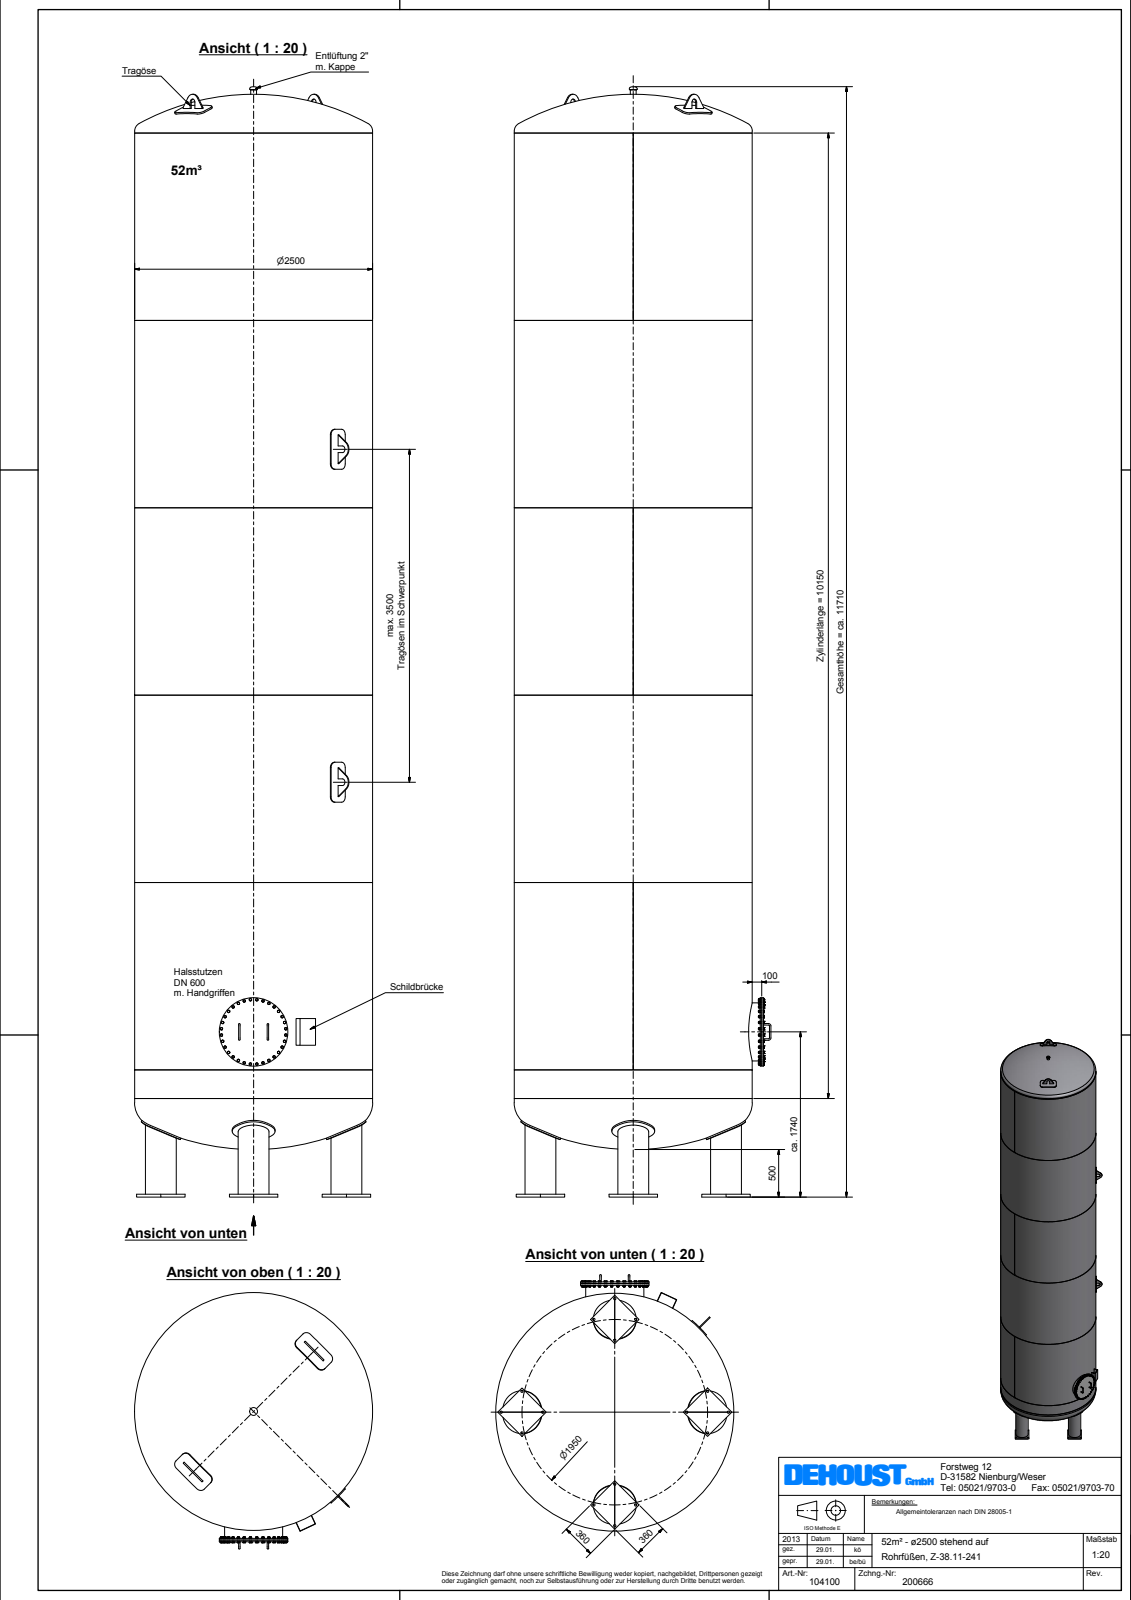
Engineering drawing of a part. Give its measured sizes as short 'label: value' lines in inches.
name: Beh\S\dlter_Z-38_11-241_2500_052_KV
written by: Autodesk Inventor 2012 (AUTOMOTIVE_DESIGN)
unit: in
bodies: 6 solids, 210 faces (119 planar, 61 cylindrical, 30 other)
size: 456.448 × 103.11 × 98.425
volume: 150 100 in³; area: 295 600 in²
holes: 4× ⌀7.874, 4× ⌀12.083, 1× ⌀2.374, 1× ⌀23.543, 1× ⌀97.638, 1× ⌀97.874, 1× ⌀97.953
bosses: 4× ⌀17.717, 4× ⌀12.752, 1× ⌀98.425, 1× ⌀28.346, 1× ⌀24.016
rounds: 16× R2.205, 3× R1.378, 3× R3.346, 1× R49.606
face distances: 40.809, 1.181, 39.628, 0.63, 14.171, 54.278, 0.116, 6.968, 0.115, 0.394
hole spacings: 38.386, 54.286, 76.772
